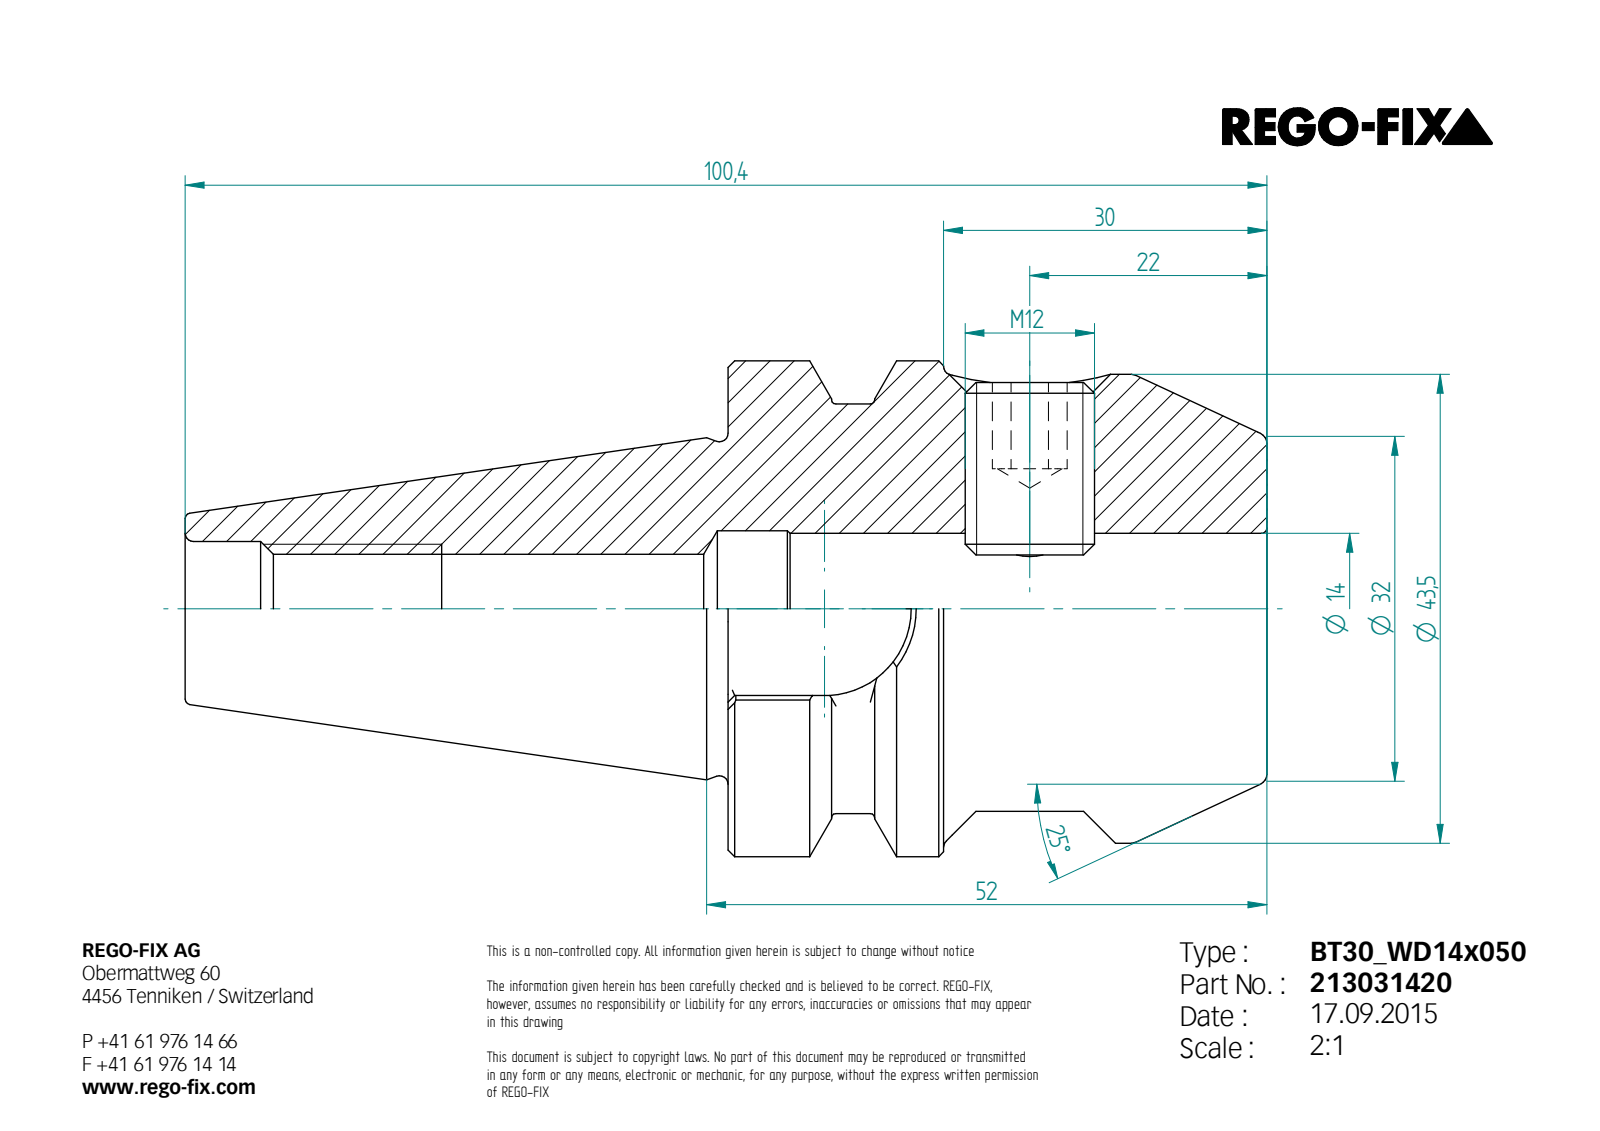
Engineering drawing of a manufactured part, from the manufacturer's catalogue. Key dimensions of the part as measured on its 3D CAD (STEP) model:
STEP written by: Unknown (AUTOMOTIVE_DESIGN)
Units: millimetres
Bodies: 2 solids, 111 faces (49 planar, 23 cylindrical, 39 other)
Overall size (bounding box): 100.4 × 46 × 46
Volume: 80 641 mm³ · Surface area: 18 258 mm²
Round holes (diameter × count): ⌀10.11 ×2, ⌀12.5 ×1, ⌀14 ×1, ⌀14.5 ×1
Round bosses / shafts (diameter × count): ⌀46 ×1, ⌀43.5 ×1, ⌀12 ×1
Partial cylindrical surfaces — rounded edges, fillets, slot ends (radius × count): R0.5 ×8, R8.05 ×1, R19 ×1
Main face-to-face distances: 50, 32.5, 6, 23.8, 26.85, 3.05, 10.75, 13.05, 16.1, 50.4
